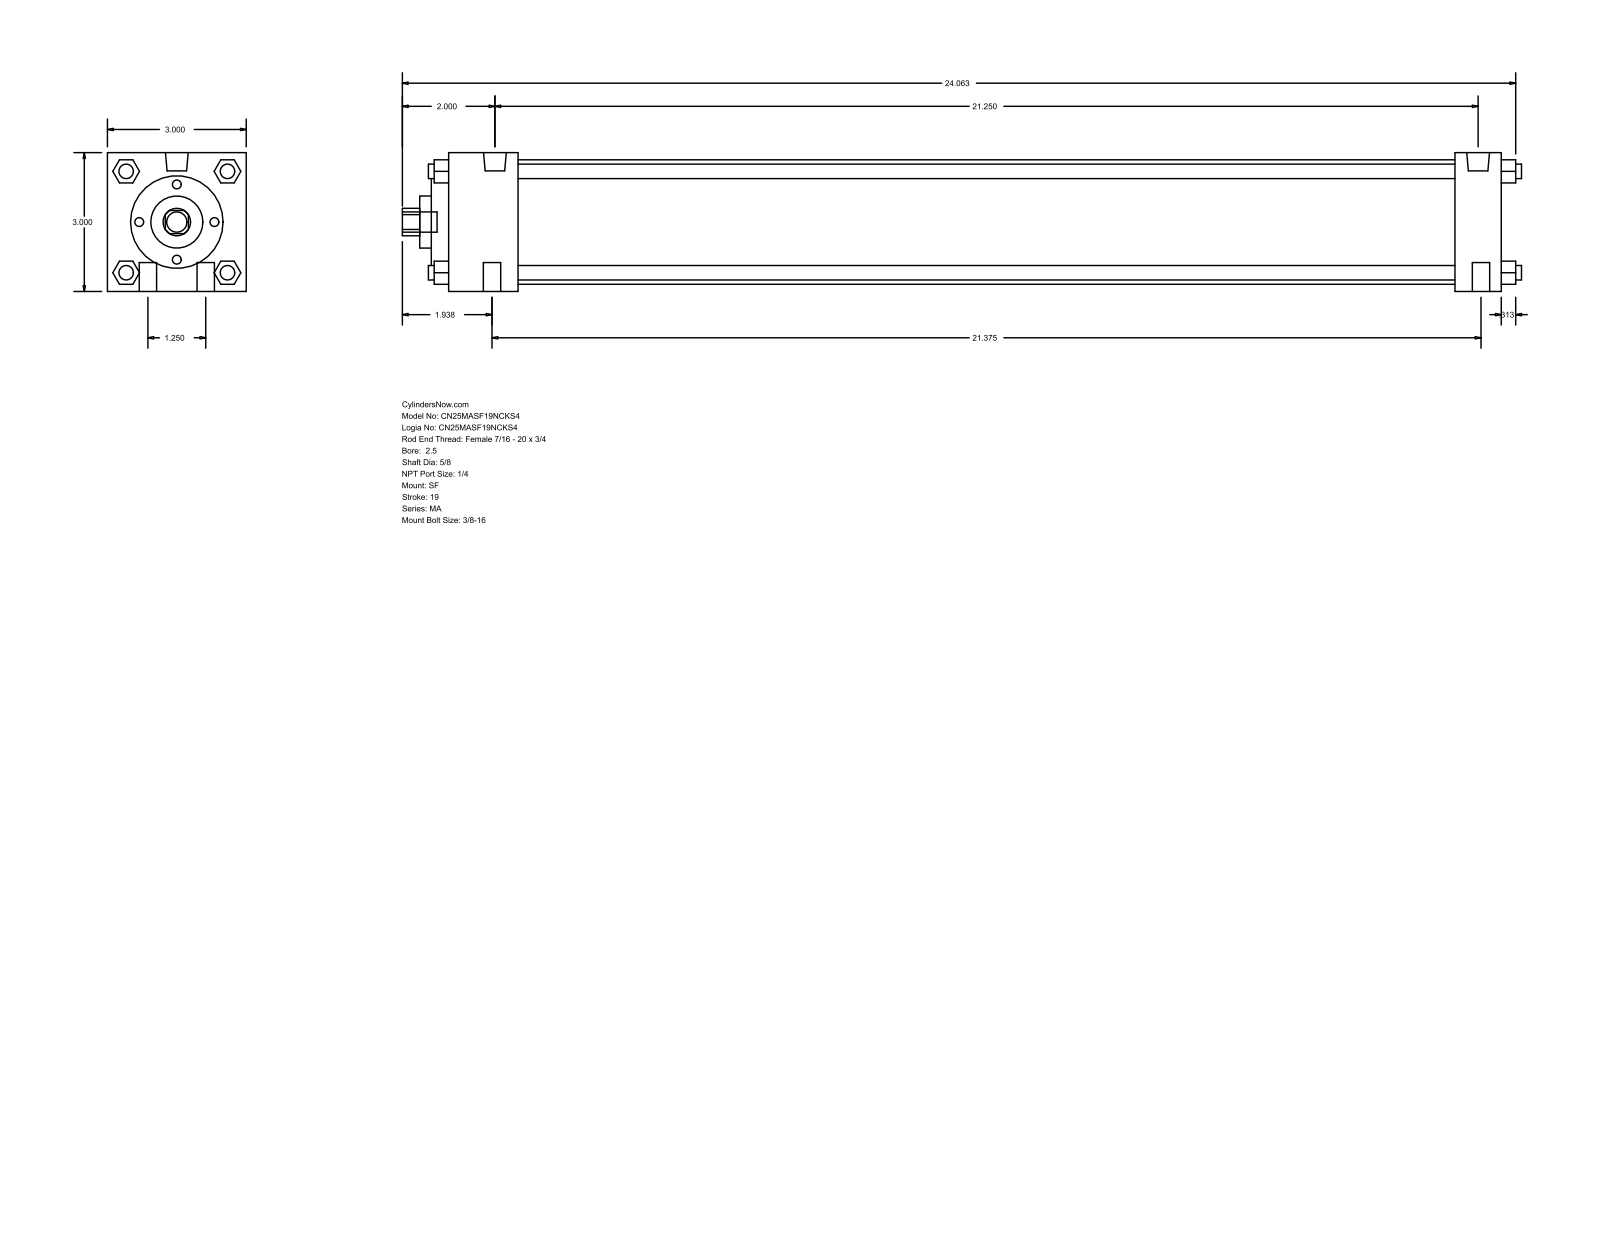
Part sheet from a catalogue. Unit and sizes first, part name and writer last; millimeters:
Units: millimetres
Overall size (bounding box): 614.36 × 76.2 × 76.2
Round holes (diameter × count): ⌀15.88 ×1, ⌀28.57 ×1, ⌀50.8 ×1, ⌀68.33 ×1
Round bosses / shafts (diameter × count): ⌀7.94 ×6, ⌀9.53 ×4, ⌀12.49 ×2, ⌀11.11 ×1
Partial cylindrical surfaces — rounded edges, fillets, slot ends (radius × count): R7.54 ×1
Main face-to-face distances: 76.2, 577.85, 25.4, 552.45, 38.1, 514.35, 539.75, 12.7, 9.52, 47.62
Bodies: 0 solids, 126 faces (95 planar, 31 cylindrical, 0 other)
Part name (STEP PRODUCT): MA_SF__0250_0.625
STEP written by: GSSL Pune (CONFIG_CONTROL_DESIGN)
